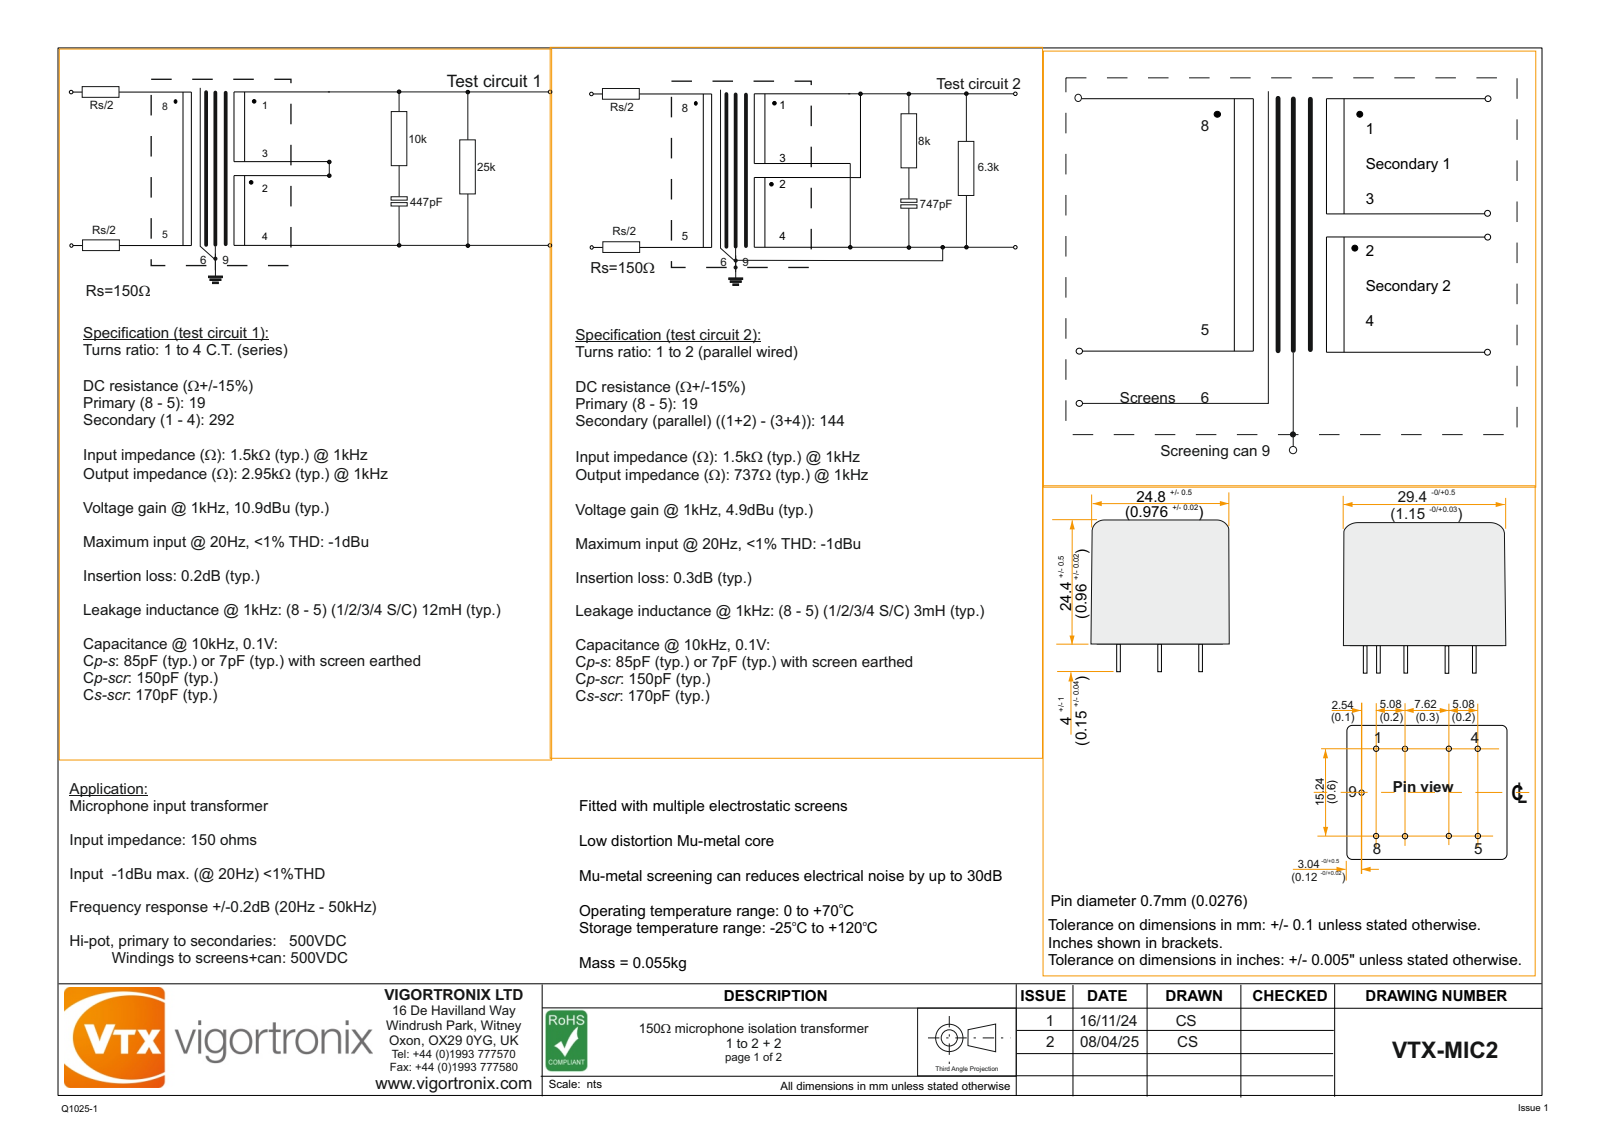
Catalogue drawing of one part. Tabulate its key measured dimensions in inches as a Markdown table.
| quantity | value |
| --- | --- |
| part name | VTX-MIC2 BOBBIN; VTX-MIC2 CAN; VTX-MIC2 LID; VTX-MIC2 |
| STEP written by | SolidWorks 2024 (AUTOMOTIVE_DESIGN) |
| units | inches |
| bodies | 3 solids, 130 faces (36 planar, 74 cylindrical, 20 other) |
| overall size | 1.166 × 1.126 × 0.993 |
| volume | 0.935 in³ |
| surface area | 16.83 in² |
| round holes (diameter × count) | 0.138 × 8, 0.059 × 1 |
| round bosses / shafts (diameter × count) | 0.028 × 8 |
| partial cylindrical surfaces (radius × count) | 0.02 × 20, 0.075 × 8, 0.098 × 8, 0.079 × 4 |
| main face-to-face distances | 0.024, 0.921, 0.898, 0.886, 0.035, 0.909, 0.945, 0.906, 1.083, 0.102 |
| hole center spacings | 0.2, 0.5, 0.6, 0.632, 0.671, 0.781, 0.3, 0.316 |
